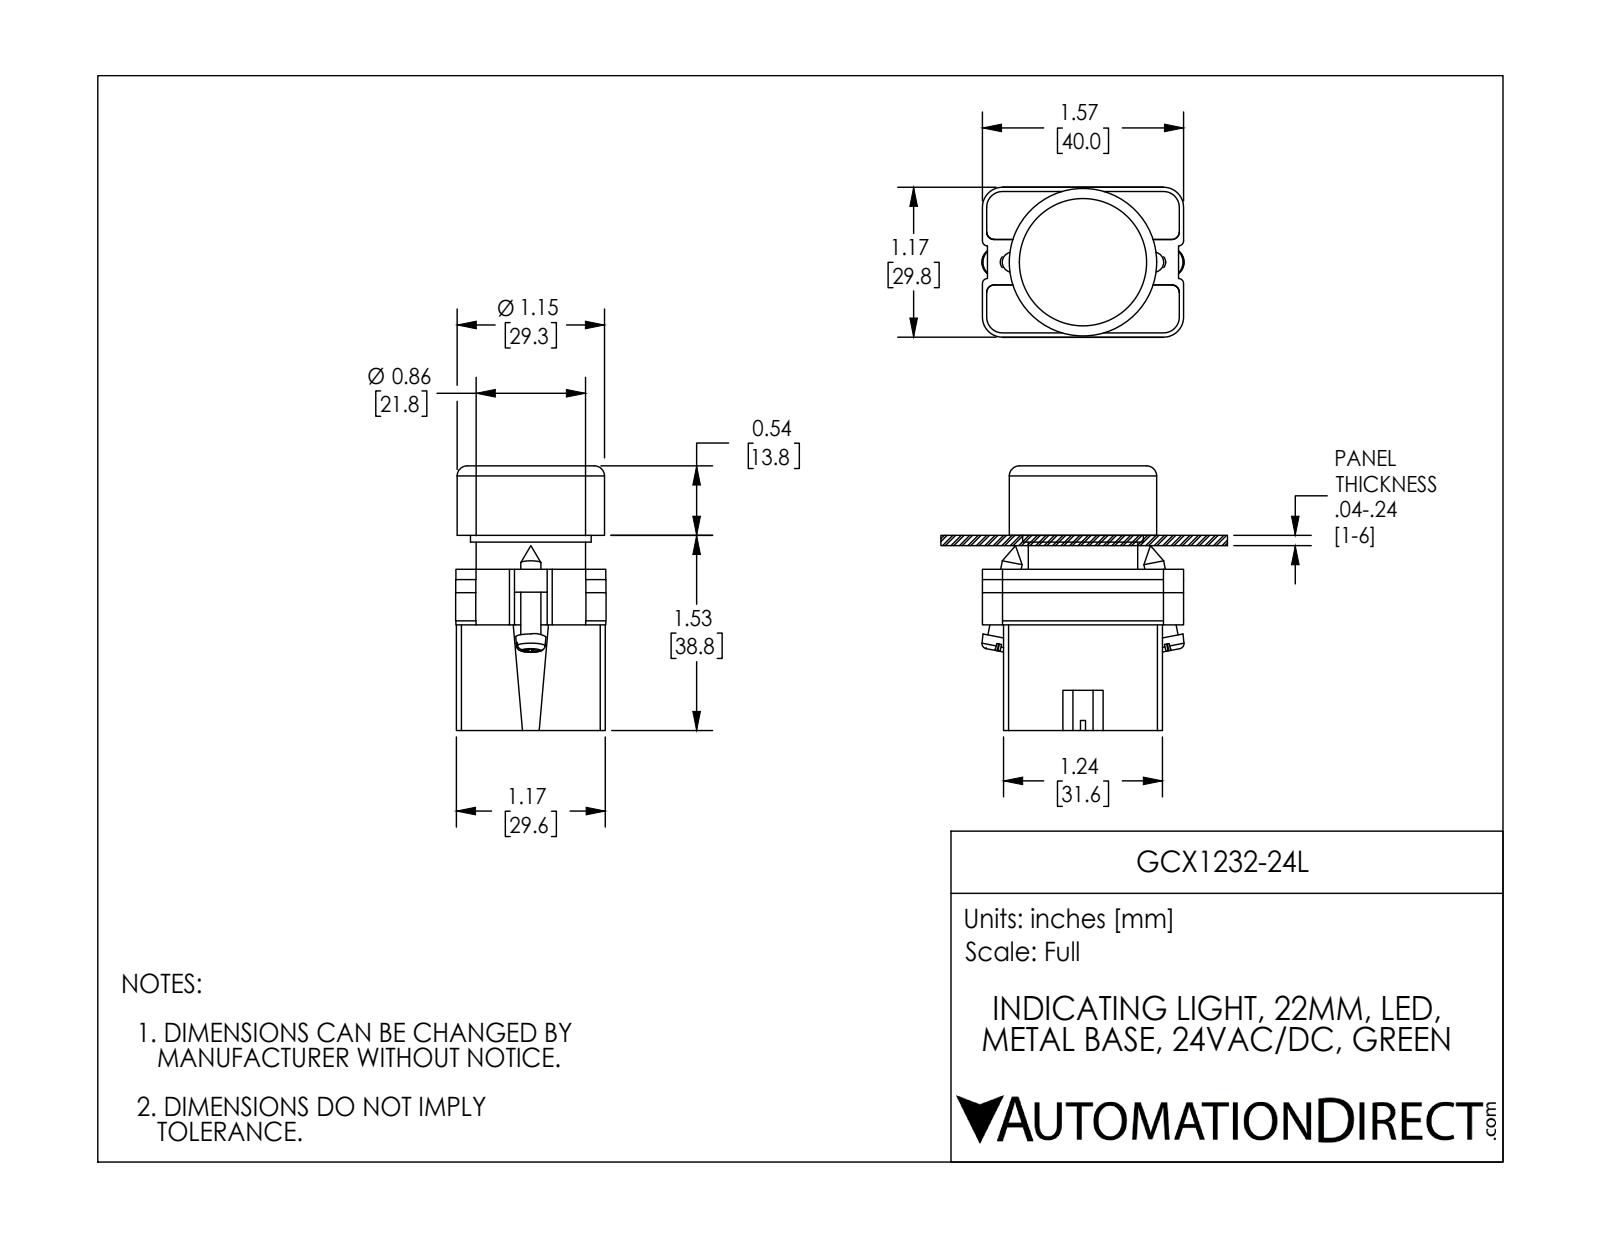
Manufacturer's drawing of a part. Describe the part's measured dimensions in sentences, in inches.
The part is named "ecx1029; ECX1050; GCX1232L OPERATOR; GCX1232-24L". Its 3-D file was written by "SolidWorks 2016 (AUTOMOTIVE_DESIGN)". It is 7 solids with 339 faces: 178 planar, 134 cylindrical and 27 other. Overall it measures 2.071 by 1.581 by 1.177 inches. Its volume is 2.268 cubic inches and its surface area 31.19 square inches. Round holes: 2 of diameter 0.124, 2 of diameter 0.13, 1 of diameter 0.197, 1 of diameter 0.469, 1 of diameter 0.852, 1 of diameter 0.878, 1 of diameter 0.888, 1 of diameter 1.102. Round bosses or shafts: 4 of diameter 0.157, 1 of diameter 1.154, 1 of diameter 1.092, 1 of diameter 0.945, 1 of diameter 0.856, 1 of diameter 0.78, 1 of diameter 0.504. Partial cylindrical surfaces (rounded edges, fillets, slot ends): 24 of radius 0.059, 12 of radius 0.041, 12 of radius 0.124, 12 of radius 0.157, 8 of radius 0.039, 2 of radius 0.128, 1 of radius 0.392, 1 of radius 0.398. The main face-to-face distances are 0.86, 1.244, 0.827, 1.687, 1.136, 0.033, 1.963, 0.276, 0.031, 1.165.
